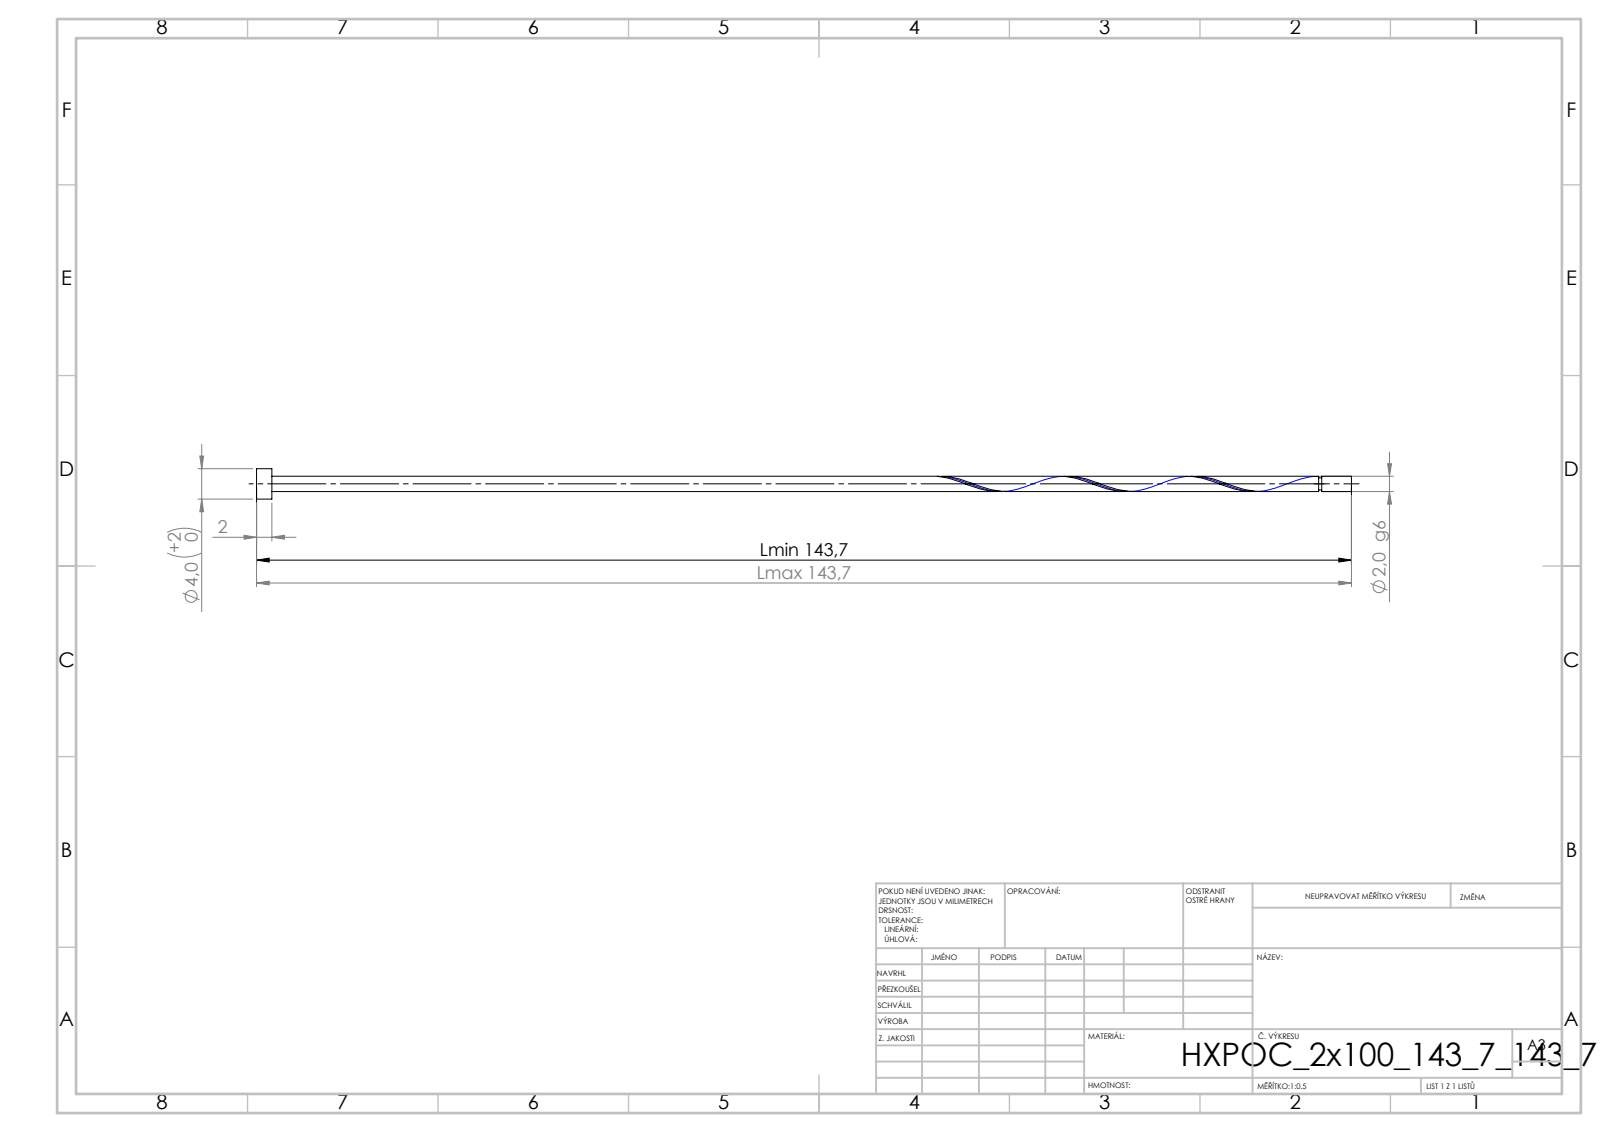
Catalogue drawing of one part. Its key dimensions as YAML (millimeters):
step_written_by: "SolidWorks 2019 (CONFIG_CONTROL_DESIGN)"
units: millimeters
bodies: {solids: 1, faces: 21, planar: 6, cylindrical: 14, other: 1}
overall_size: [143.7, 4, 4]
volume: 467
surface_area: 953
round_bosses_or_shafts:
  - {diameter: 4, count: 1}
  - {diameter: 2, count: 1}
  - {diameter: 1.6, count: 1}
face_to_face_distances: [2, 143.7, 141.7, 139.8, 137.8, 3.9, 139.4, 137.4, 0.4, 4.3]
